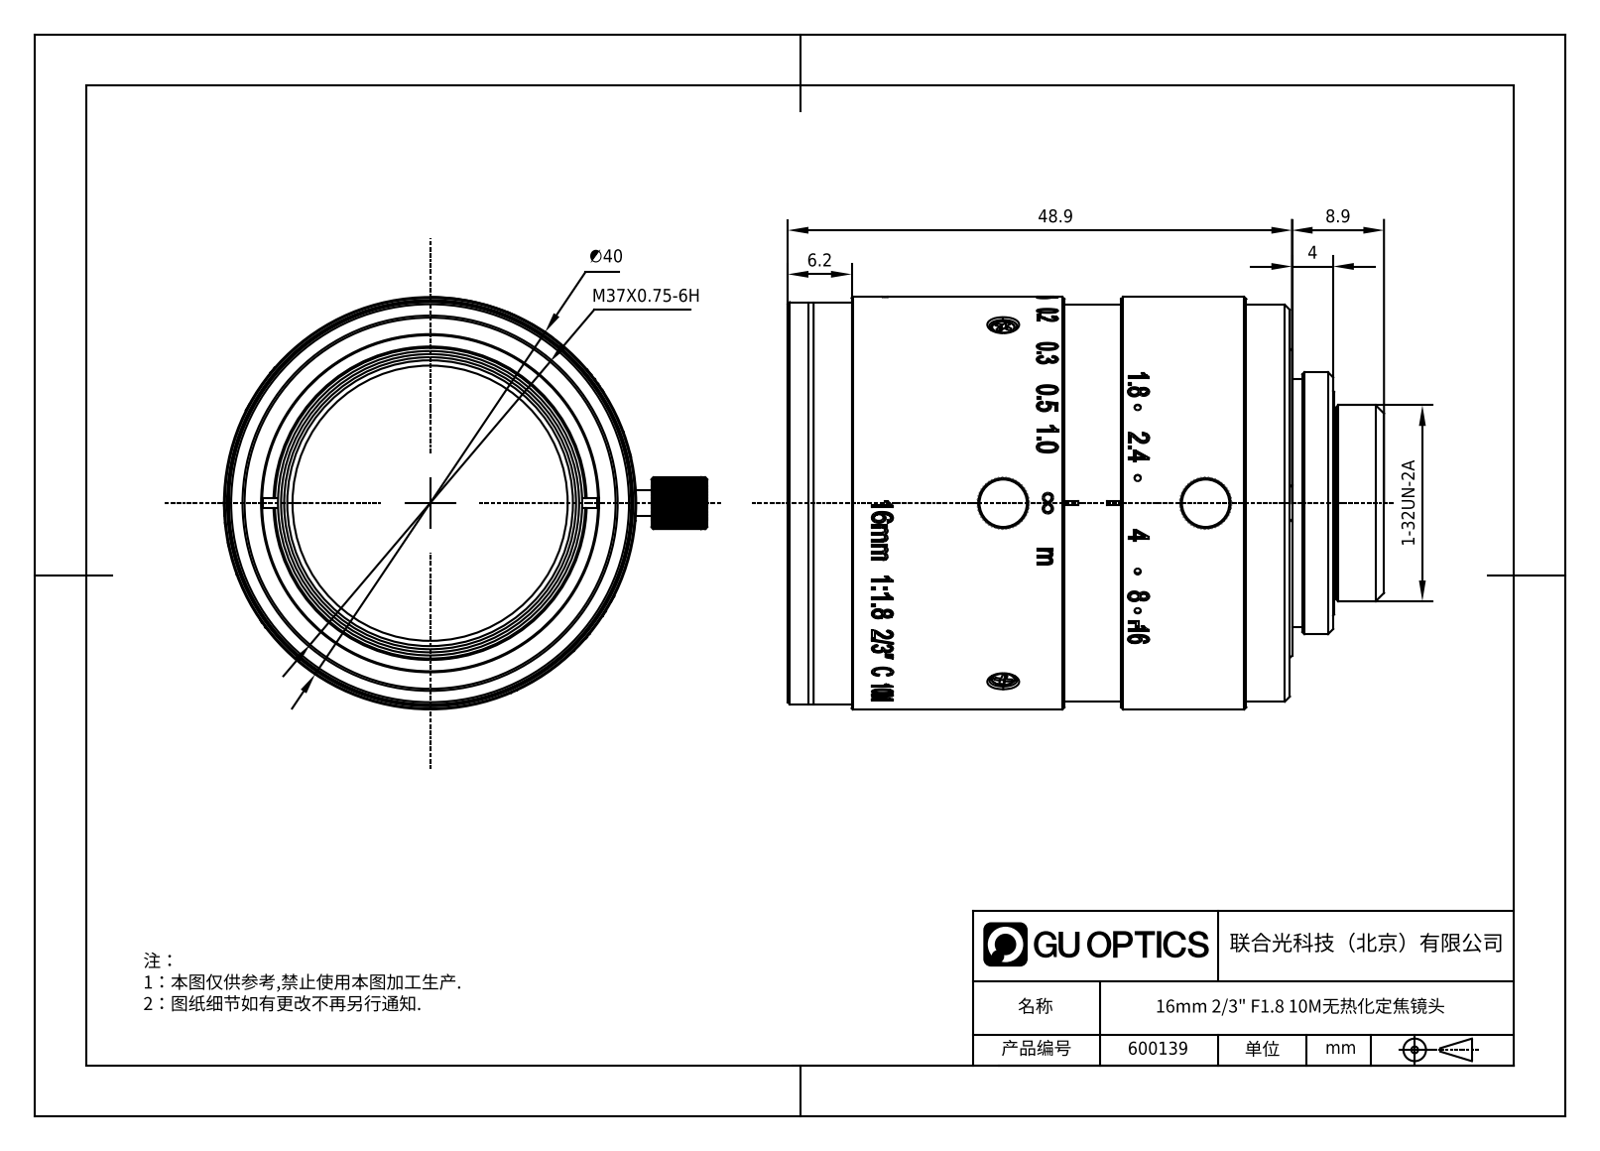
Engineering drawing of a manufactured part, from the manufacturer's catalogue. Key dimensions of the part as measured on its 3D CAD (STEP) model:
Part name (STEP PRODUCT): V330031B-606.stp; ADMI4DCC9D9B2L3R_12.stp; ADMI4DCC9D9B2L3R_15.stp; ADMI4DCC9D9B2L3R_2.stp (+8 more)
STEP written by: SolidWorks 2020 (CONFIG_CONTROL_DESIGN)
Units: millimetres
Bodies: 19 solids, 2042 faces (768 planar, 360 cylindrical, 914 other)
Overall size (bounding box): 57.85 × 46.99 × 40
Volume: 29 990 mm³ · Surface area: 31 858 mm²
Round holes (diameter × count): ⌀0.6 ×7, ⌀3.2 ×4, ⌀1.3 ×3, ⌀1.5 ×3, ⌀1.8 ×3, ⌀2 ×3, ⌀2.7 ×3, ⌀1.6 ×1, ⌀10.5 ×1, ⌀12.5 ×1, ⌀14 ×1, ⌀14.4 ×1
Round bosses / shafts (diameter × count): ⌀2.5 ×4, ⌀2.9 ×3, ⌀1.7 ×3, ⌀1.4 ×3, ⌀40 ×1, ⌀39 ×1, ⌀39 ×1, ⌀38.5 ×1
Partial cylindrical surfaces — rounded edges, fillets, slot ends (radius × count): R2.45 ×6, R1.5 ×2, R2.5 ×2, R19.9 ×1
Main face-to-face distances: 2.63, 25.34, 13.88, 15.88, 2, 7.5, 2.73, 4.73, 11.15, 8.93
Hole centre spacings: 14.5, 19.64, 25.12, 4.7, 14.94
